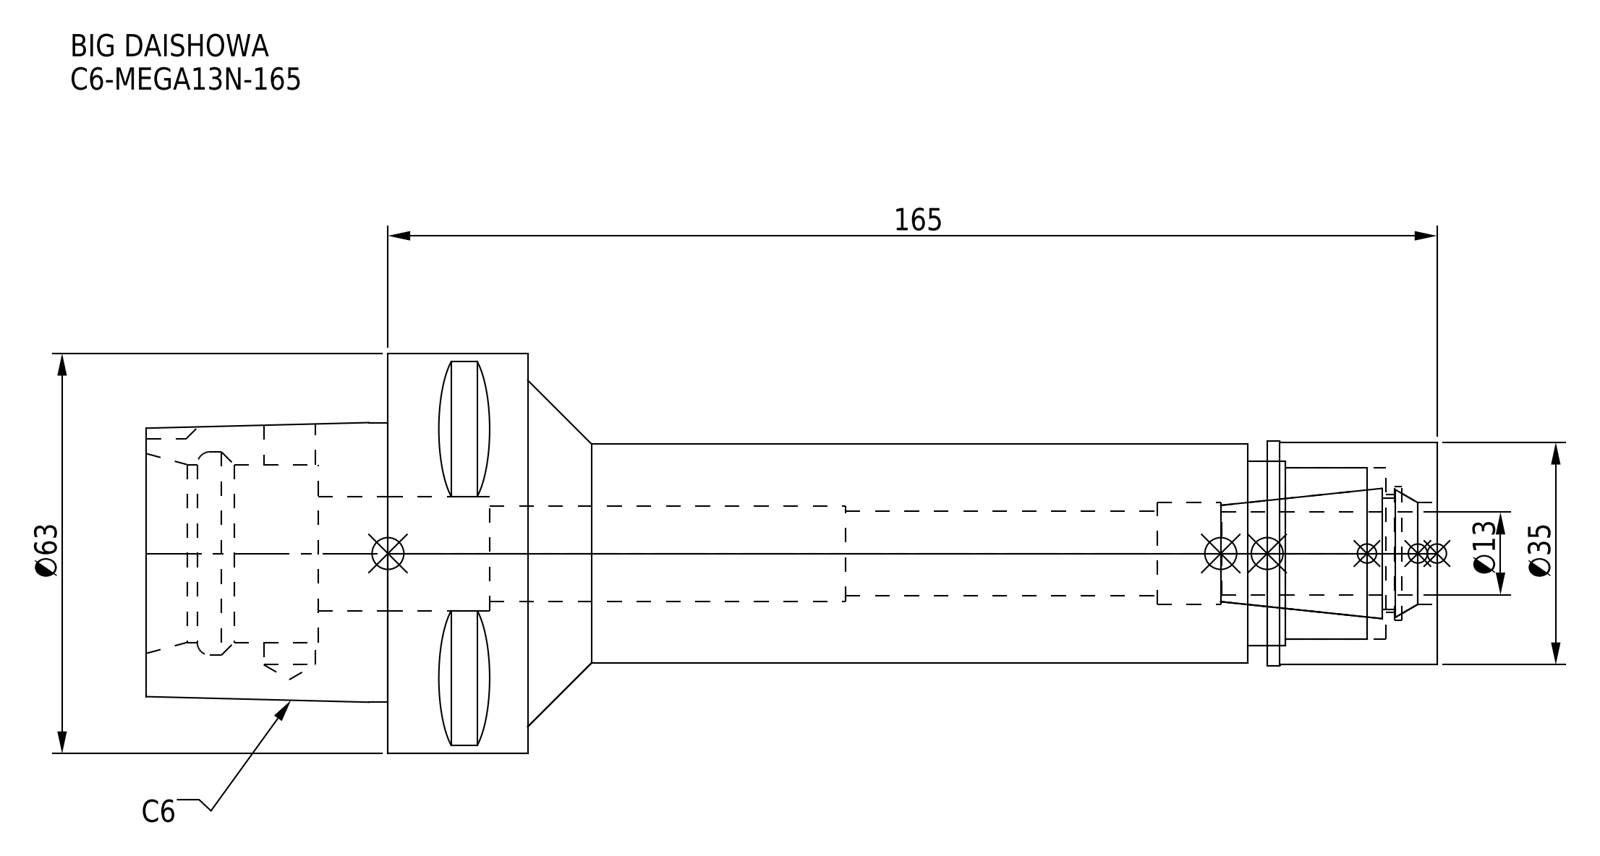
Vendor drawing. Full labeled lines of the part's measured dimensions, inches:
Part name (STEP PRODUCT): MGN13_1.stp; DXF_TEMP_ASSY_ASM_4_ASM.stp; C6-MEGA13N-165-130-FreeParts; C6-MEGA13N-165-130.stp (+3 more)
STEP written by: SolidWorks 2019 (CONFIG_CONTROL_DESIGN)
Units: inches
Bodies: 2 solids, 98 faces (39 planar, 41 cylindrical, 18 other)
Overall size (bounding box): 7.992 × 2.48 × 2.48
Volume: 12.73 in³ · Surface area: 71.71 in²
Round holes (diameter × count): ⌀0.319 ×1, ⌀0.524 ×1, ⌀0.591 ×1, ⌀0.63 ×1, ⌀0.709 ×1, ⌀0.728 ×1, ⌀0.827 ×1, ⌀1.063 ×1, ⌀1.102 ×1, ⌀1.142 ×1, ⌀1.26 ×1
Round bosses / shafts (diameter × count): ⌀2.48 ×1, ⌀1.39 ×1, ⌀1.378 ×1, ⌀1.358 ×1
Partial cylindrical surfaces — rounded edges, fillets, slot ends (radius × count): R0.197 ×1
Main face-to-face distances: 6.496, 0.866, 5.63, 0.433, 7.992, 2.362, 1.496, 1.063, 1.299, 6.929
